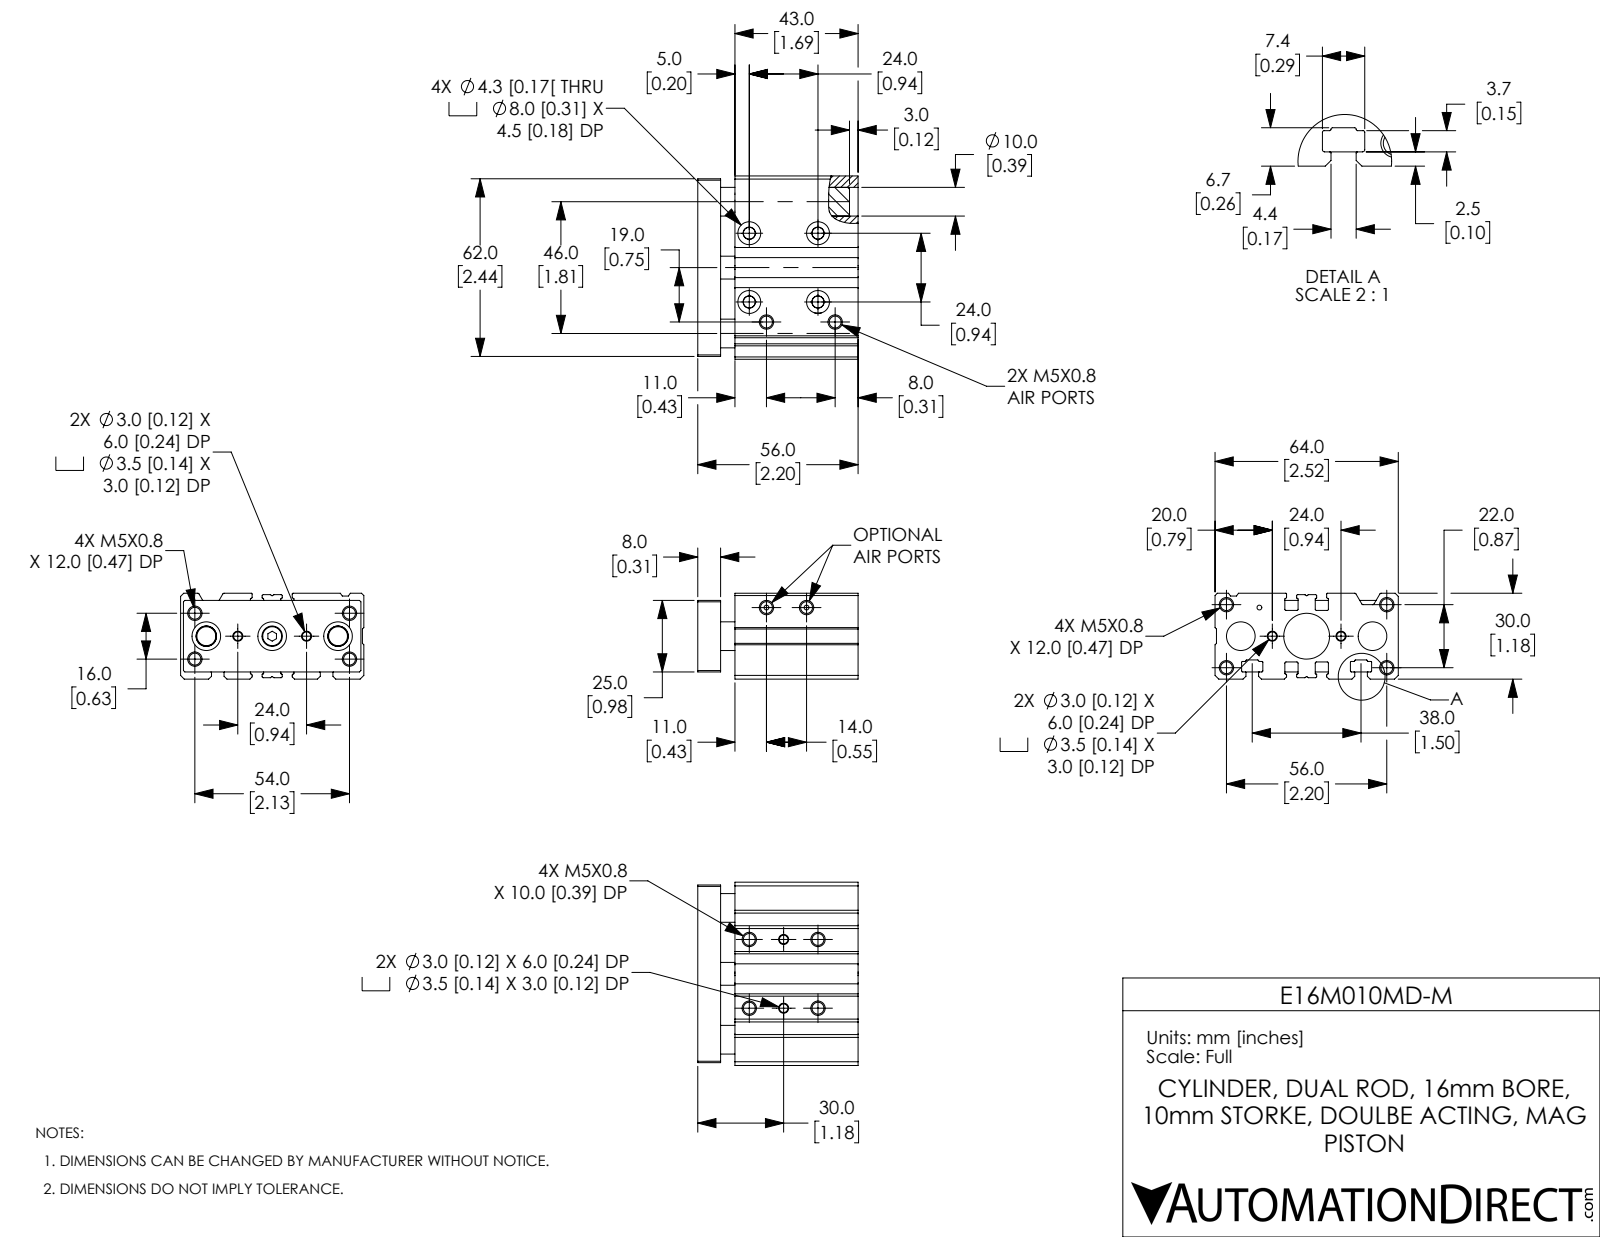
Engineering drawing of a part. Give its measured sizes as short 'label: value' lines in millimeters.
name: E16M010MD-M_BODY; E16M010MD-M; E16M010MD-M_ENDPLATE
written by: SolidWorks 2019 (CONFIG_CONTROL_DESIGN)
unit: mm
bodies: 5 solids, 411 faces (133 planar, 192 cylindrical, 86 other)
size: 64 × 56 × 30
volume: 79 357 mm³; area: 34 135 mm²
holes: 16× ⌀4.13, 4× ⌀3, 4× ⌀3.5, 4× ⌀4.3, 4× ⌀8, 3× ⌀1.67, 3× ⌀5, 3× ⌀10, 2× ⌀7.11, 1× ⌀10, 1× ⌀16, 1× ⌀16
bosses: 1× ⌀8, 1× ⌀7.11
rounds: 22× R0.2, 20× R0.4, 8× R0.25, 6× R0.3, 4× R0.5
face distances: 27.5, 48, 0.5, 5, 13, 30, 8, 56, 43, 4
hole spacings: 24, 12, 3.16, 8.94, 12.08, 17, 19.03, 19.42
